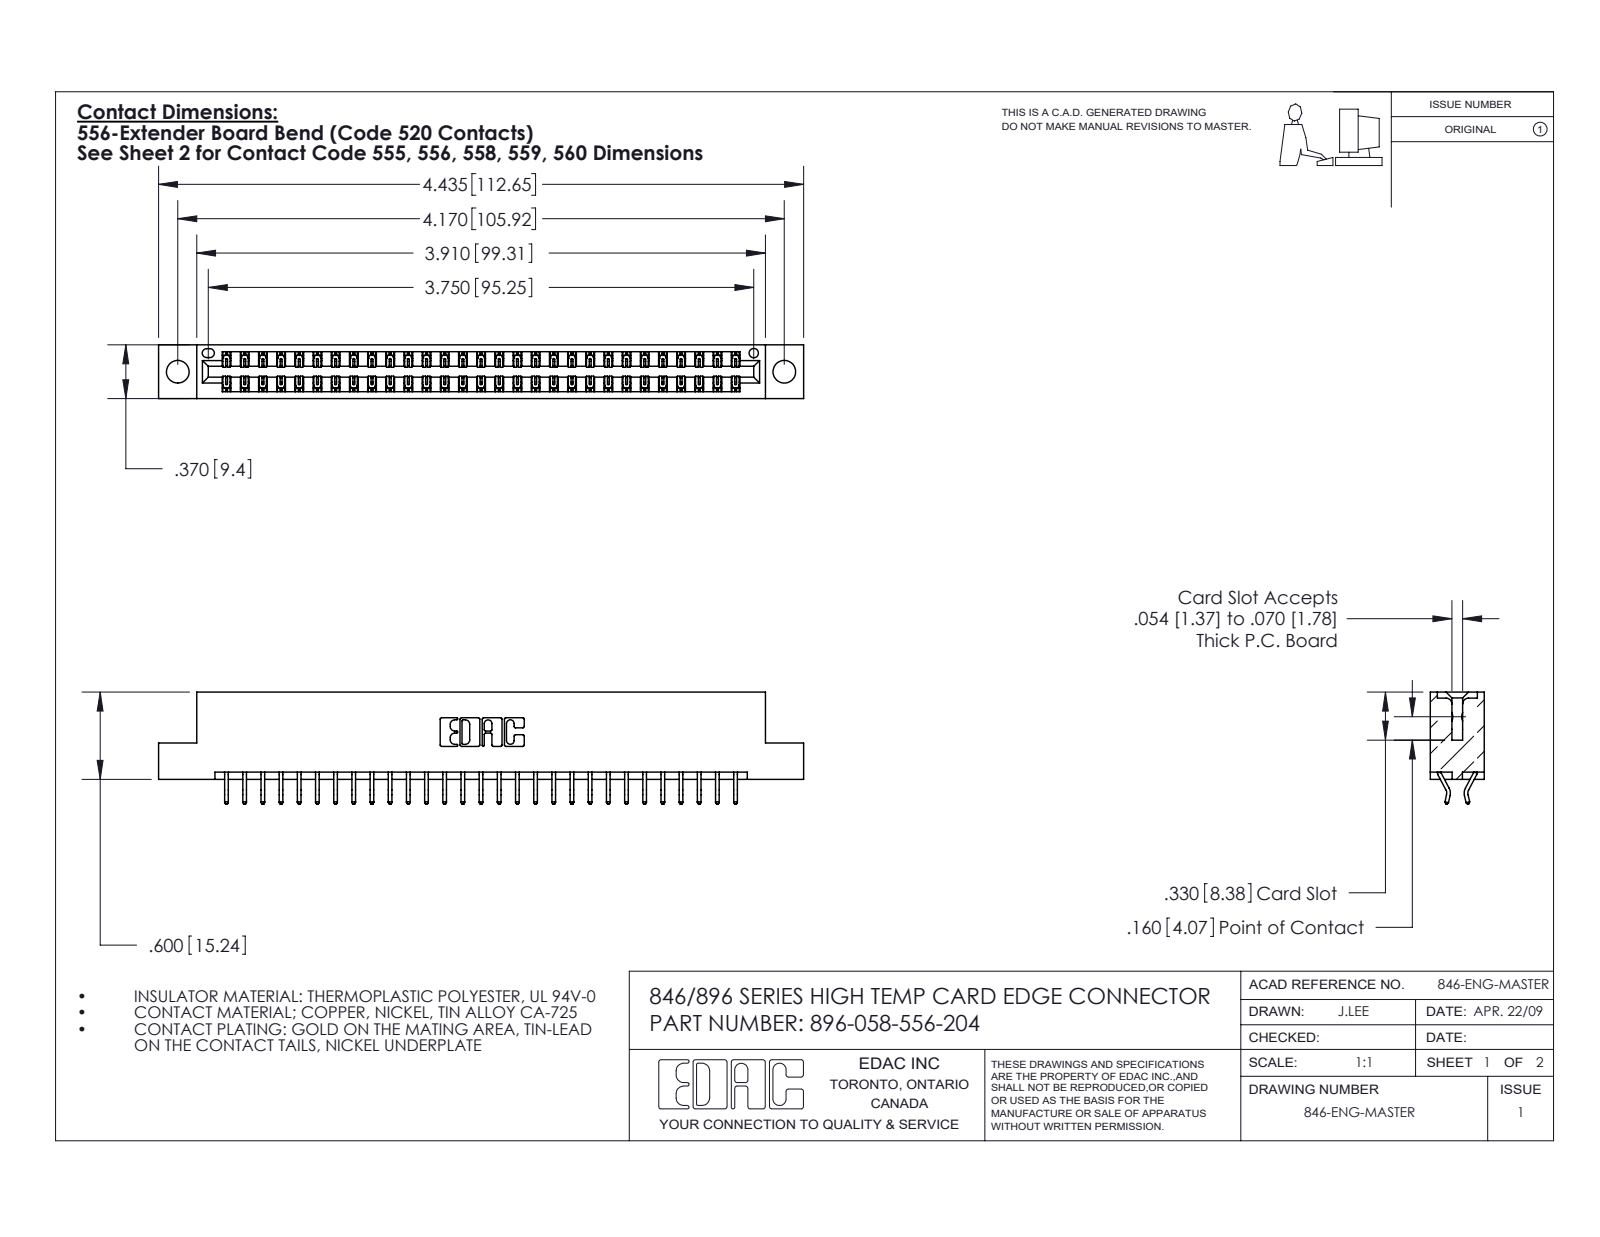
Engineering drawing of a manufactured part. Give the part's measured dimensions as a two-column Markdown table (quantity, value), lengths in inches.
| quantity | value |
| --- | --- |
| part name | 396-058-556-204; 345-292-001_556 Tail; 346 Part_Flush Mounting Lugs - 0.156 Dia-TH |
| STEP written by | SolidWorks 2016 (CONFIG_CONTROL_DESIGN) |
| units | inches |
| bodies | 59 solids, 3486 faces (2338 planar, 1148 cylindrical, 0 other) |
| overall size | 4.435 × 0.77 × 0.37 |
| volume | 0.659 in³ |
| surface area | 22.31 in² |
| round holes (diameter × count) | 0.156 × 2, 0.064 × 1 |
| partial cylindrical surfaces (radius × count) | 0.006 × 87, 0.01 × 22, 0.007 × 6, 0.031 × 6, 0.026 × 3, 0.01 × 2, 0.014 × 2, 0.022 × 2 |
| main face-to-face distances | 0.048, 0.322, 0.37, 0.25, 0.025, 0.072, 0.298, 0.275, 0.148, 0.222 |
| hole center spacings | 0.246, 3.962, 4.17 |
